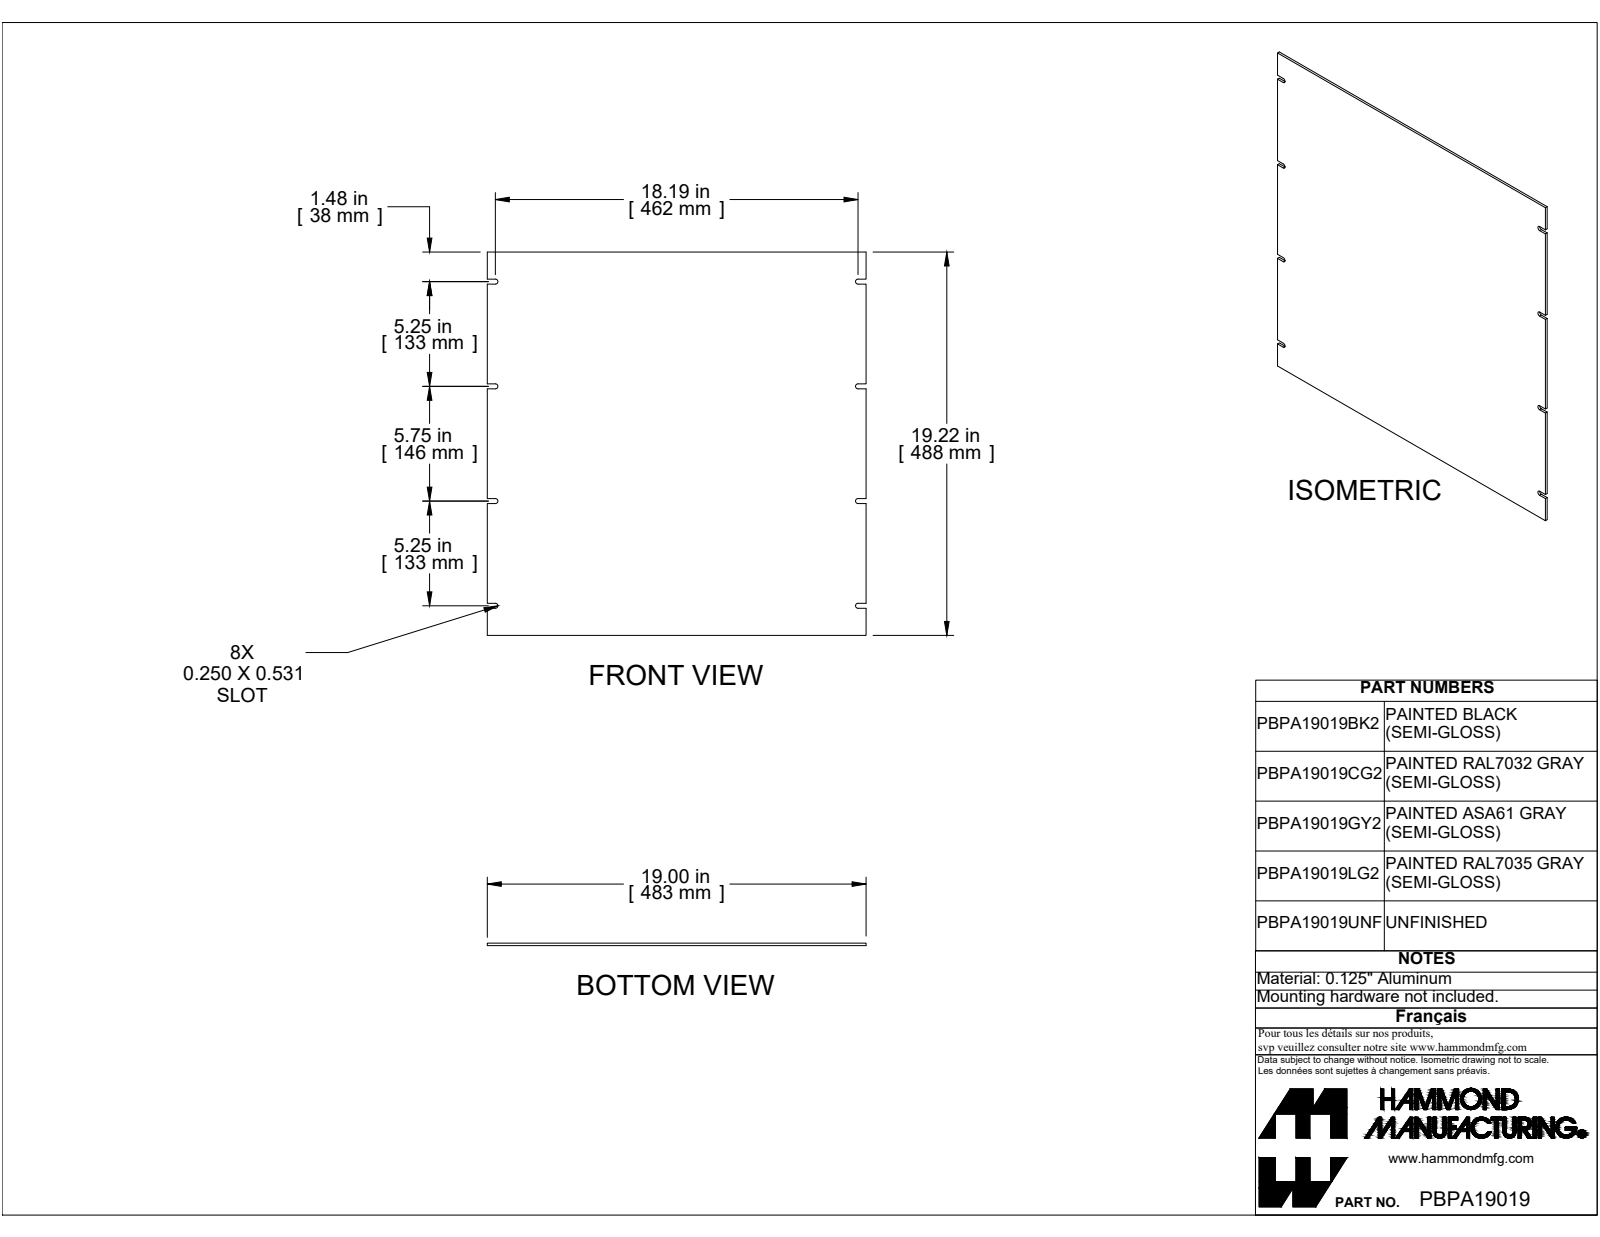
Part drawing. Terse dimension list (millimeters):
name: PBPA19019UNF
written by: SolidWorks 2019 (CONFIG_CONTROL_DESIGN)
unit: mm
bodies: 1 solid, 38 faces (30 planar, 8 cylindrical, 0 other)
size: 488.1 × 482.6 × 3.2
volume: 745 900 mm³; area: 476 600 mm²
rounds: 8× R3.2
face distances: 3.2, 488.1, 482.6, 133.4, 279.4, 6.4, 139.7, 34.5, 40.9, 167.9
